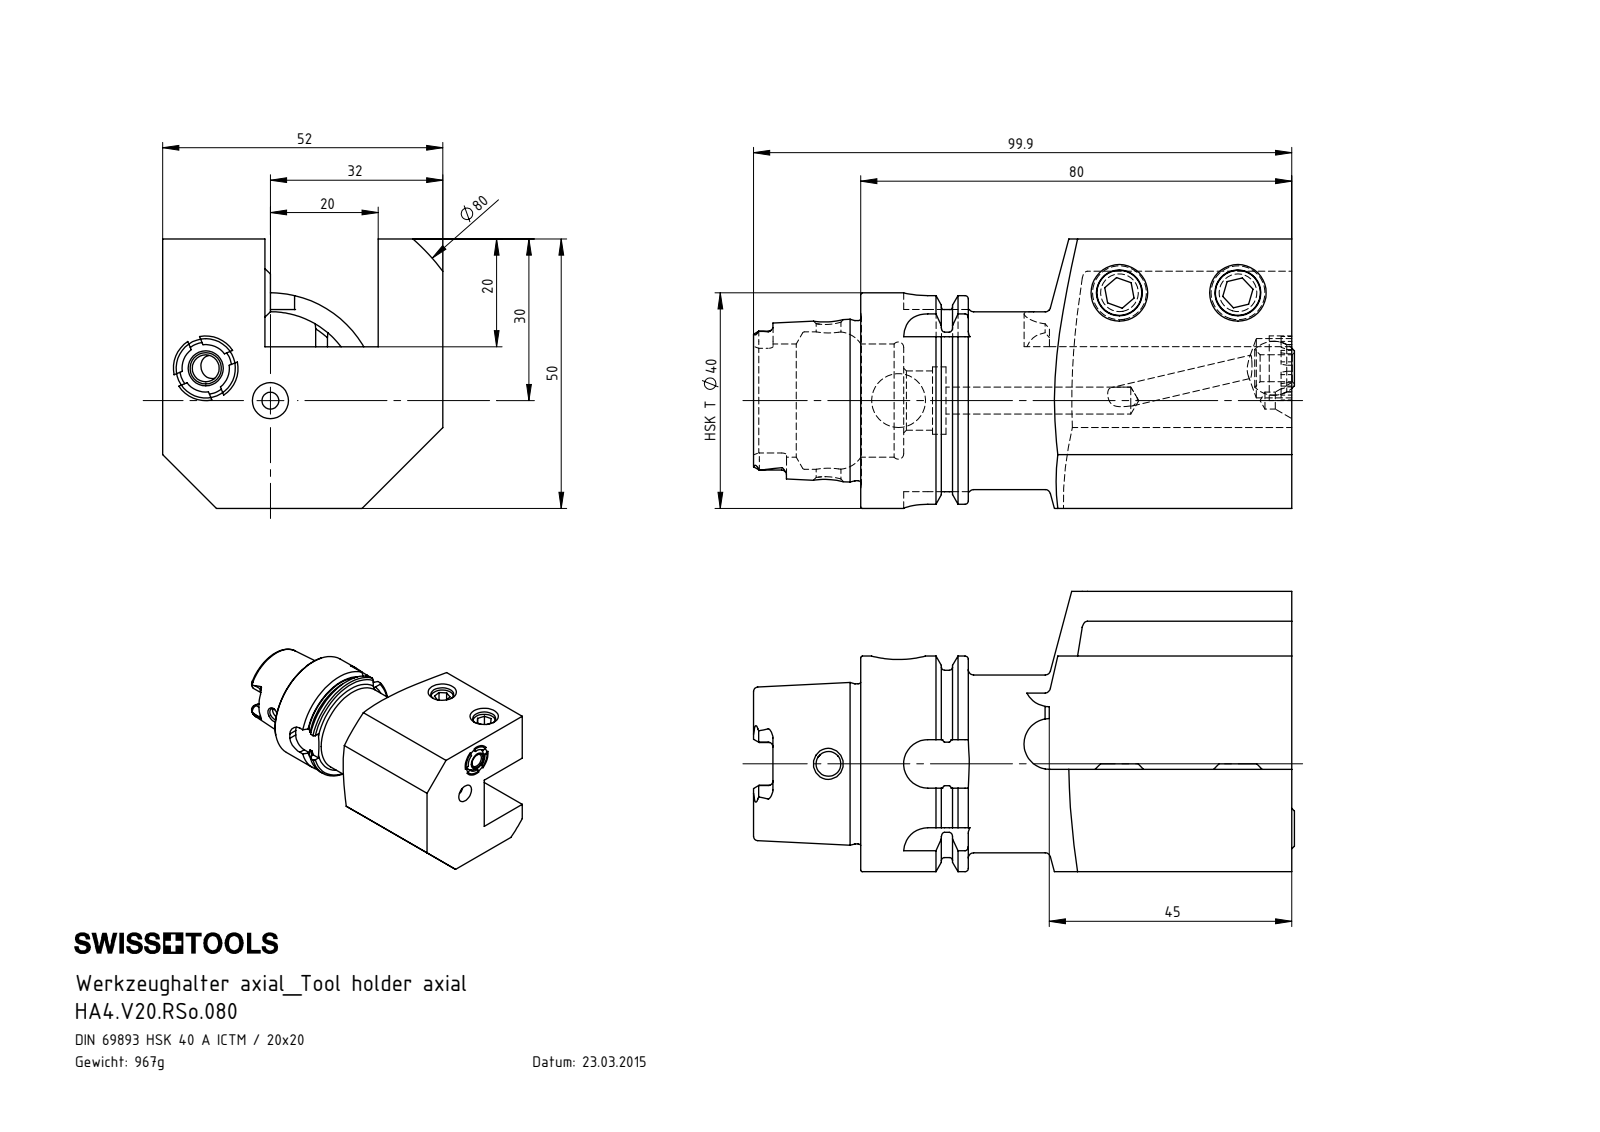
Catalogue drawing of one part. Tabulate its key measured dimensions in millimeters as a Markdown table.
| quantity | value |
| --- | --- |
| part name | HA4-V20.RSo.080; KU1-U12.003.010_A; KU1-U12.002.010_A; ISO 4026 - M10 x 18 (+1 more) |
| STEP written by | SolidWorks 2012 (CONFIG_CONTROL_DESIGN) |
| units | millimeters |
| bodies | 5 solids, 268 faces (93 planar, 74 cylindrical, 101 other) |
| overall size | 100.38 × 52 × 50 |
| volume | 123 192 mm³ |
| surface area | 27 234 mm² |
| round holes (diameter × count) | 5 × 2, 8.5 × 2, 10 × 2, 11 × 2, 3.15 × 1, 4.2 × 1, 4.6 × 1, 12.5 × 1, 21 × 1, 25.5 × 1 |
| round bosses / shafts (diameter × count) | 10 × 2, 40 × 1, 34.75 × 1, 33 × 1, 29.71 × 1, 12 × 1 |
| partial cylindrical surfaces (radius × count) | 0.9 × 6, 1.88 × 4, 4.5 × 4, 4.7 × 2, 4.4 × 1, 40 × 1 |
| main face-to-face distances | 52, 20, 50, 12, 30, 40, 33, 21, 19, 80 |
| hole center spacings | 13.42, 22, 45.62, 66.1 |
